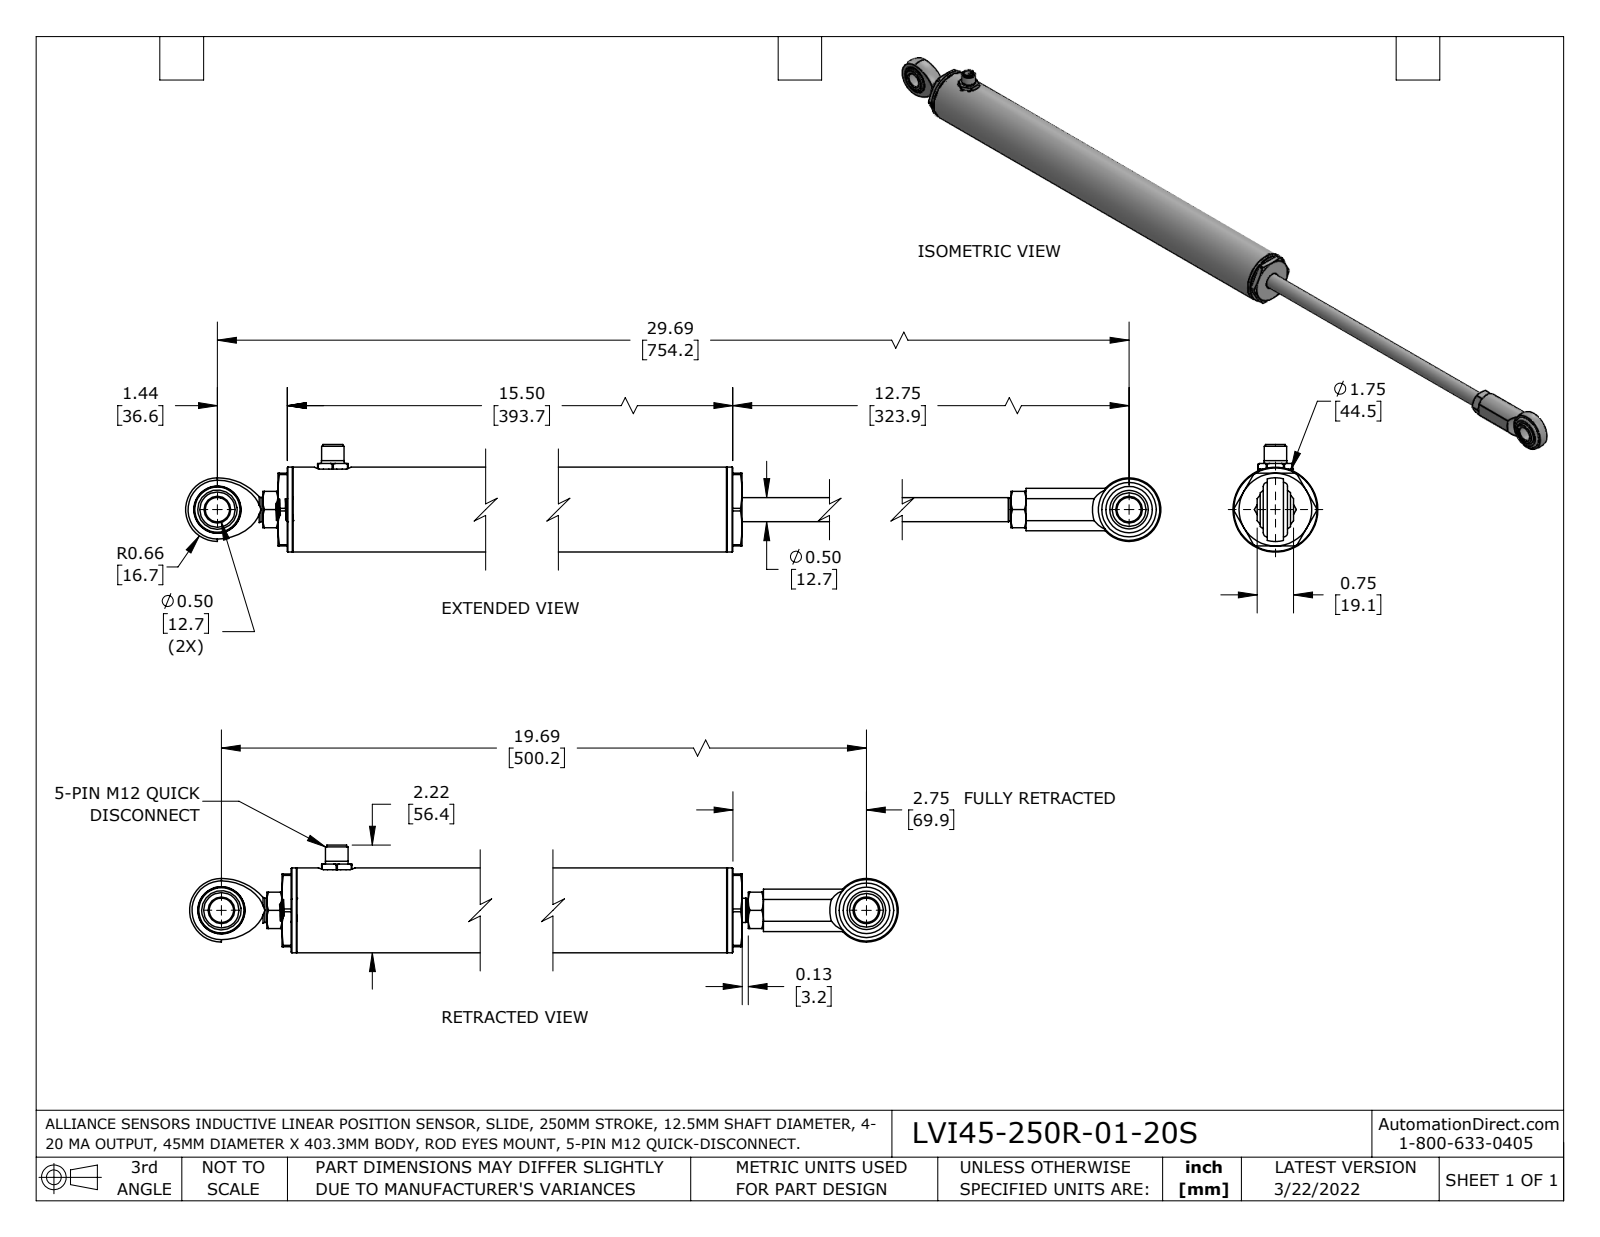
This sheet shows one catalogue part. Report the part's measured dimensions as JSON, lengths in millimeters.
{"part_name": "LVI45-250R-01-20S; 3100-0212; 3300-0003-XX_3300-0003-10; 3100-0027_98435A131 (+8 more)", "step_written_by": "SolidWorks 2021 (AUTOMOTIVE_DESIGN)", "units": "millimeters", "bodies": {"solids": 23, "faces": 873, "planar": 198, "cylindrical": 297, "other": 378}, "overall_size": [787.5, 56.4, 44.5], "volume_mm3": 310200, "surface_area_mm2": 183000, "round_holes": [[12.7, 3], [5, 1], [6.4, 1], [6.7, 1], [7.8, 1], [8.4, 1], [8.6, 1], [10.5, 1], [10.6, 1], [11.5, 1], [12.1, 1], [12.7, 1]], "round_bosses_or_shafts": [[0.8, 5], [44.5, 1], [41.3, 1], [39.7, 1], [38.9, 1], [38.1, 1], [37.3, 1], [35.2, 1]], "partial_cylinders_radius": [[8.3, 1], [9, 1], [9.6, 1], [9.7, 1], [11.1, 1], [21.6, 1]], "face_to_face_distances": [49, 12.7, 9.7, 17.5, 66.5, 344.8, 56.9, 39.4, 349.6, 332.1], "hole_center_spacings": [12.7, 754.2]}
